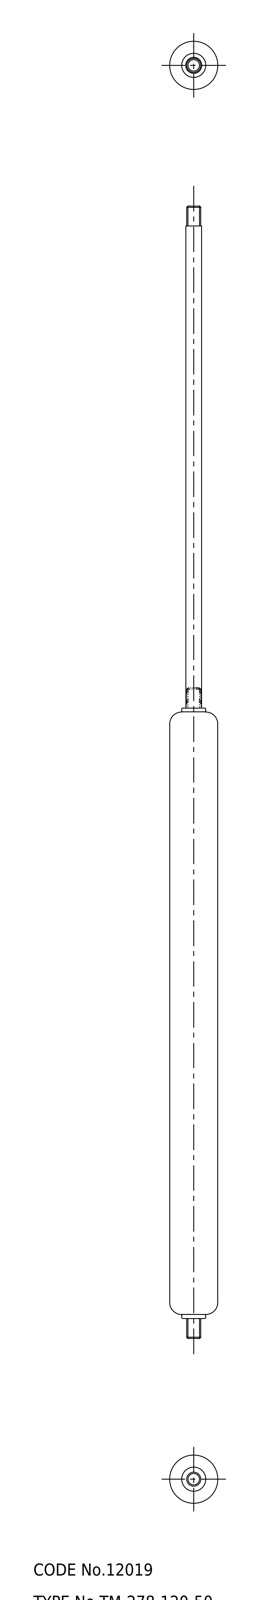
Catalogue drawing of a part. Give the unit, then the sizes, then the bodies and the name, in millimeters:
Units: millimetres
Overall size (bounding box): 282 × 12 × 12
Volume: 18 533 mm³ · Surface area: 7 490 mm²
Bodies: 2 solids, 36 faces (0 planar, 0 cylindrical, 36 other)
Part name (STEP PRODUCT): rod; TM_278_120_50_29959_36
STEP written by: CADfix (AUTOMOTIVE_DESIGN)
